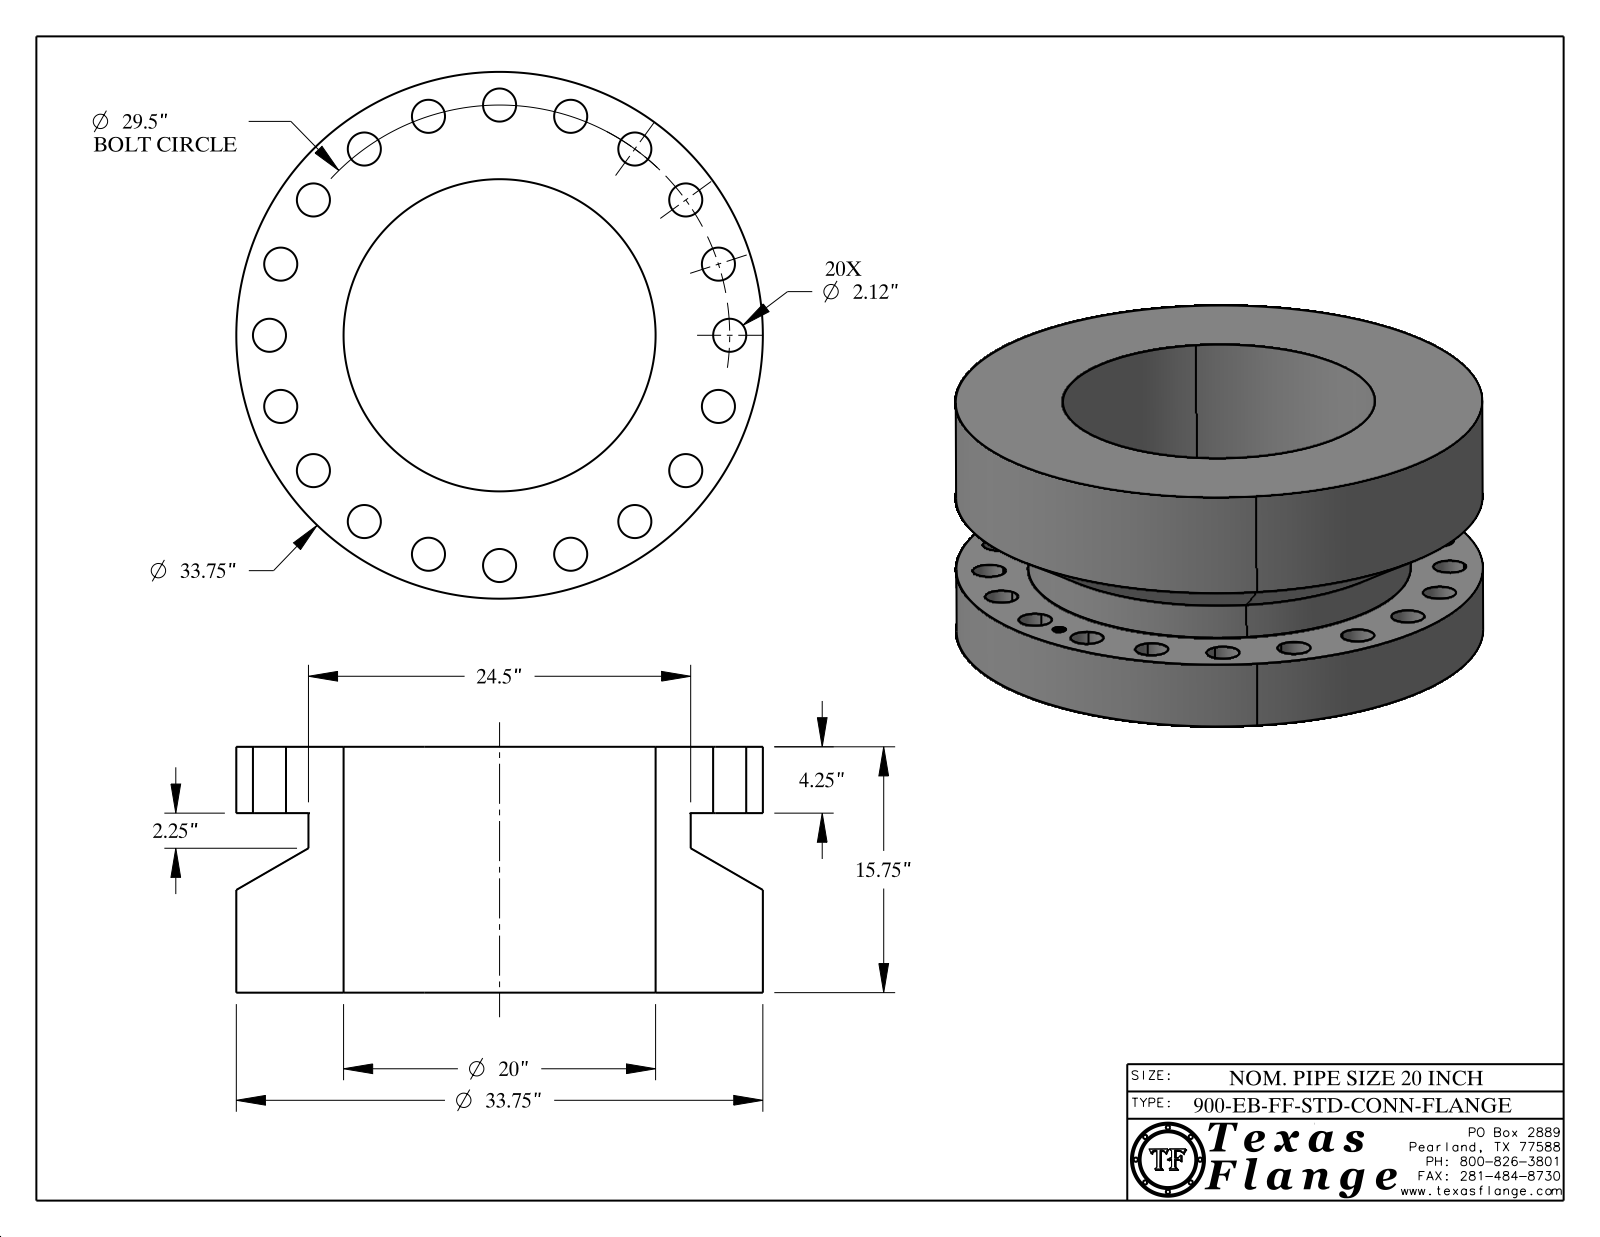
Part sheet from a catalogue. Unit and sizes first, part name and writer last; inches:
Units: inches
Overall size (bounding box): 33.75 × 33.75 × 15.75
Round holes (diameter × count): ⌀2.12 ×20, ⌀0.85 ×1, ⌀20 ×1
Round bosses / shafts (diameter × count): ⌀0.051 ×8, ⌀33.75 ×1, ⌀24.5 ×1, ⌀0.67 ×1
Main face-to-face distances: 15.75, 4.25, 11.5, 4.245, 11.505, 0.254, 0.249, 0.016, 0.046, 0.165
Hole centre spacings: 14.75, 29.137, 4.615, 17.34, 20.859, 23.866, 26.285, 9.116
Volume: 7 295 in³ · Surface area: 4 812 in²
Bodies: 1 solid, 442 faces (368 planar, 68 cylindrical, 6 other)
Part name (STEP PRODUCT): 20-900-EB-FF-STD-CONN-FLANGE
STEP written by: CATIA V5 STEP AP214 (AUTOMOTIVE_DESIGN)
